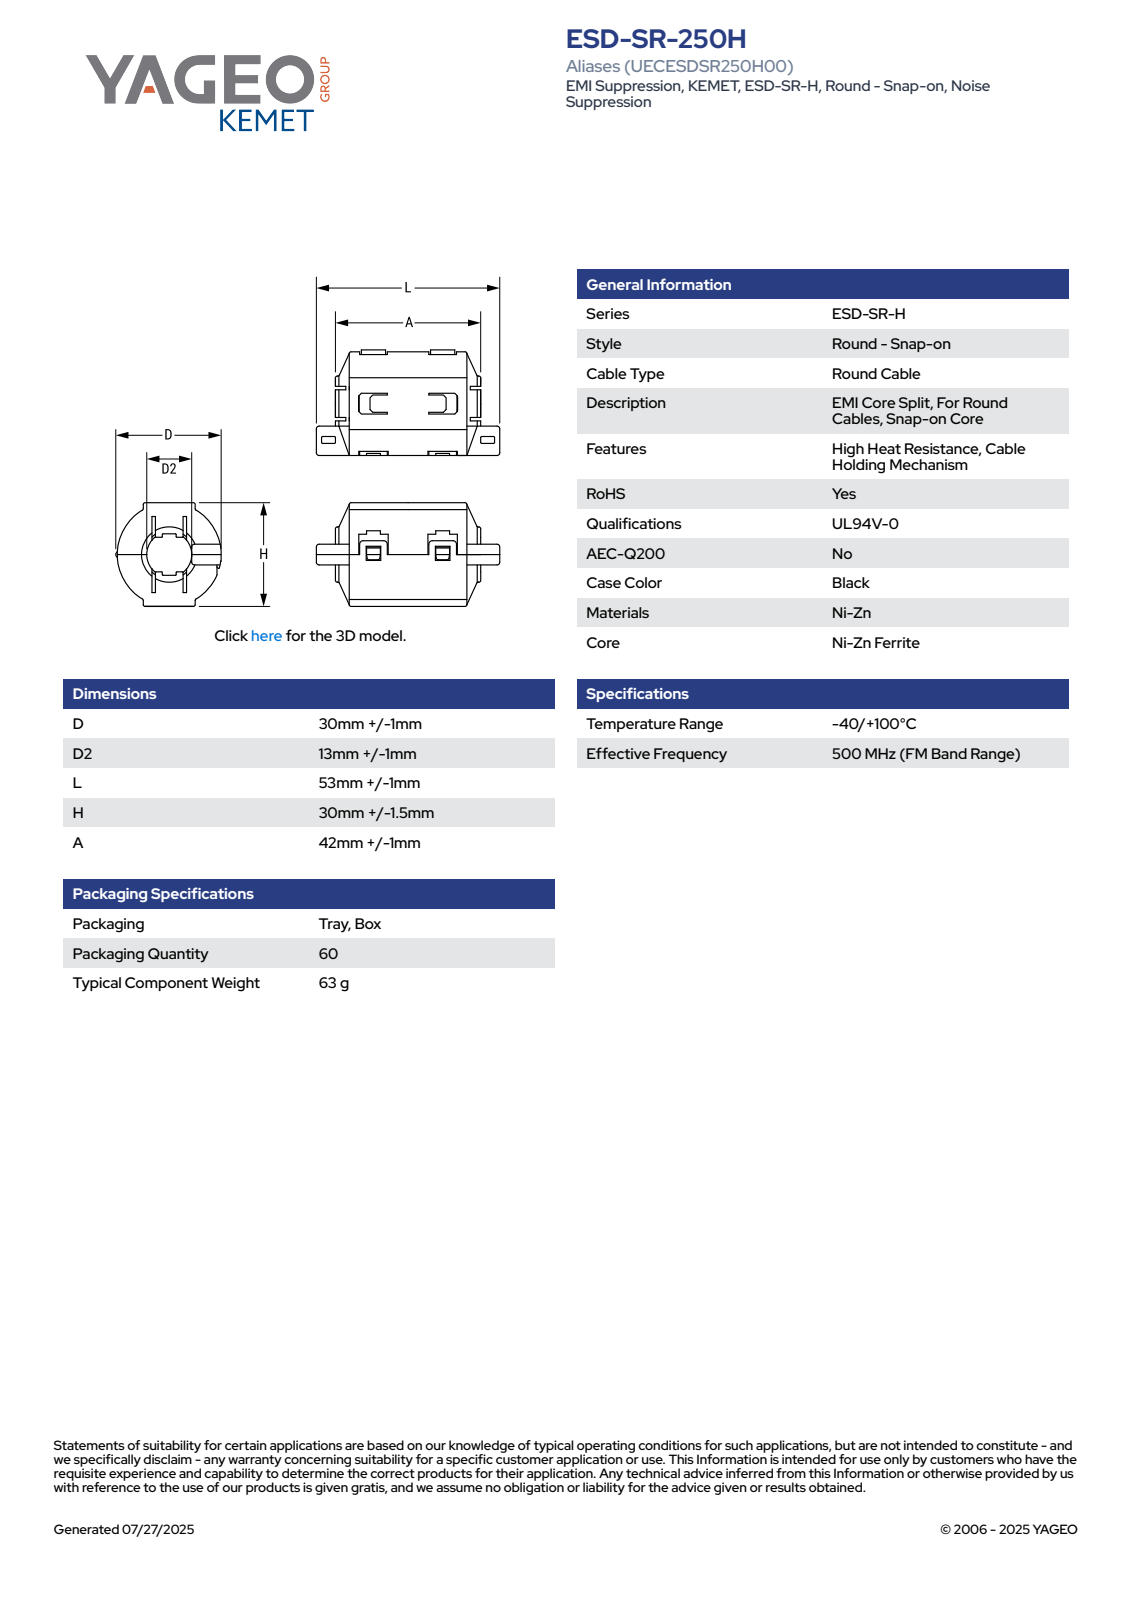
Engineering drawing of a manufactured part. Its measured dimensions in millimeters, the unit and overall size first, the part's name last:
Units: millimetres
Overall size (bounding box): 54 × 31.5 × 31.5
Partial cylindrical surfaces — rounded edges, fillets, slot ends (radius × count): R1 ×8, R4.85 ×2, R15.75 ×1
Main face-to-face distances: 31.5, 19.47, 12.03, 11.53, 7.94, 19.97, 2.5, 40.5, 43, 38
Volume: 28 446 mm³ · Surface area: 7 264 mm²
Bodies: 1 solid, 94 faces (76 planar, 14 cylindrical, 4 other)
Part name (STEP PRODUCT): EC_ESDSRH_D213L54D31H31.5A43
STEP written by: SolidWorks 2021 (AUTOMOTIVE_DESIGN)
